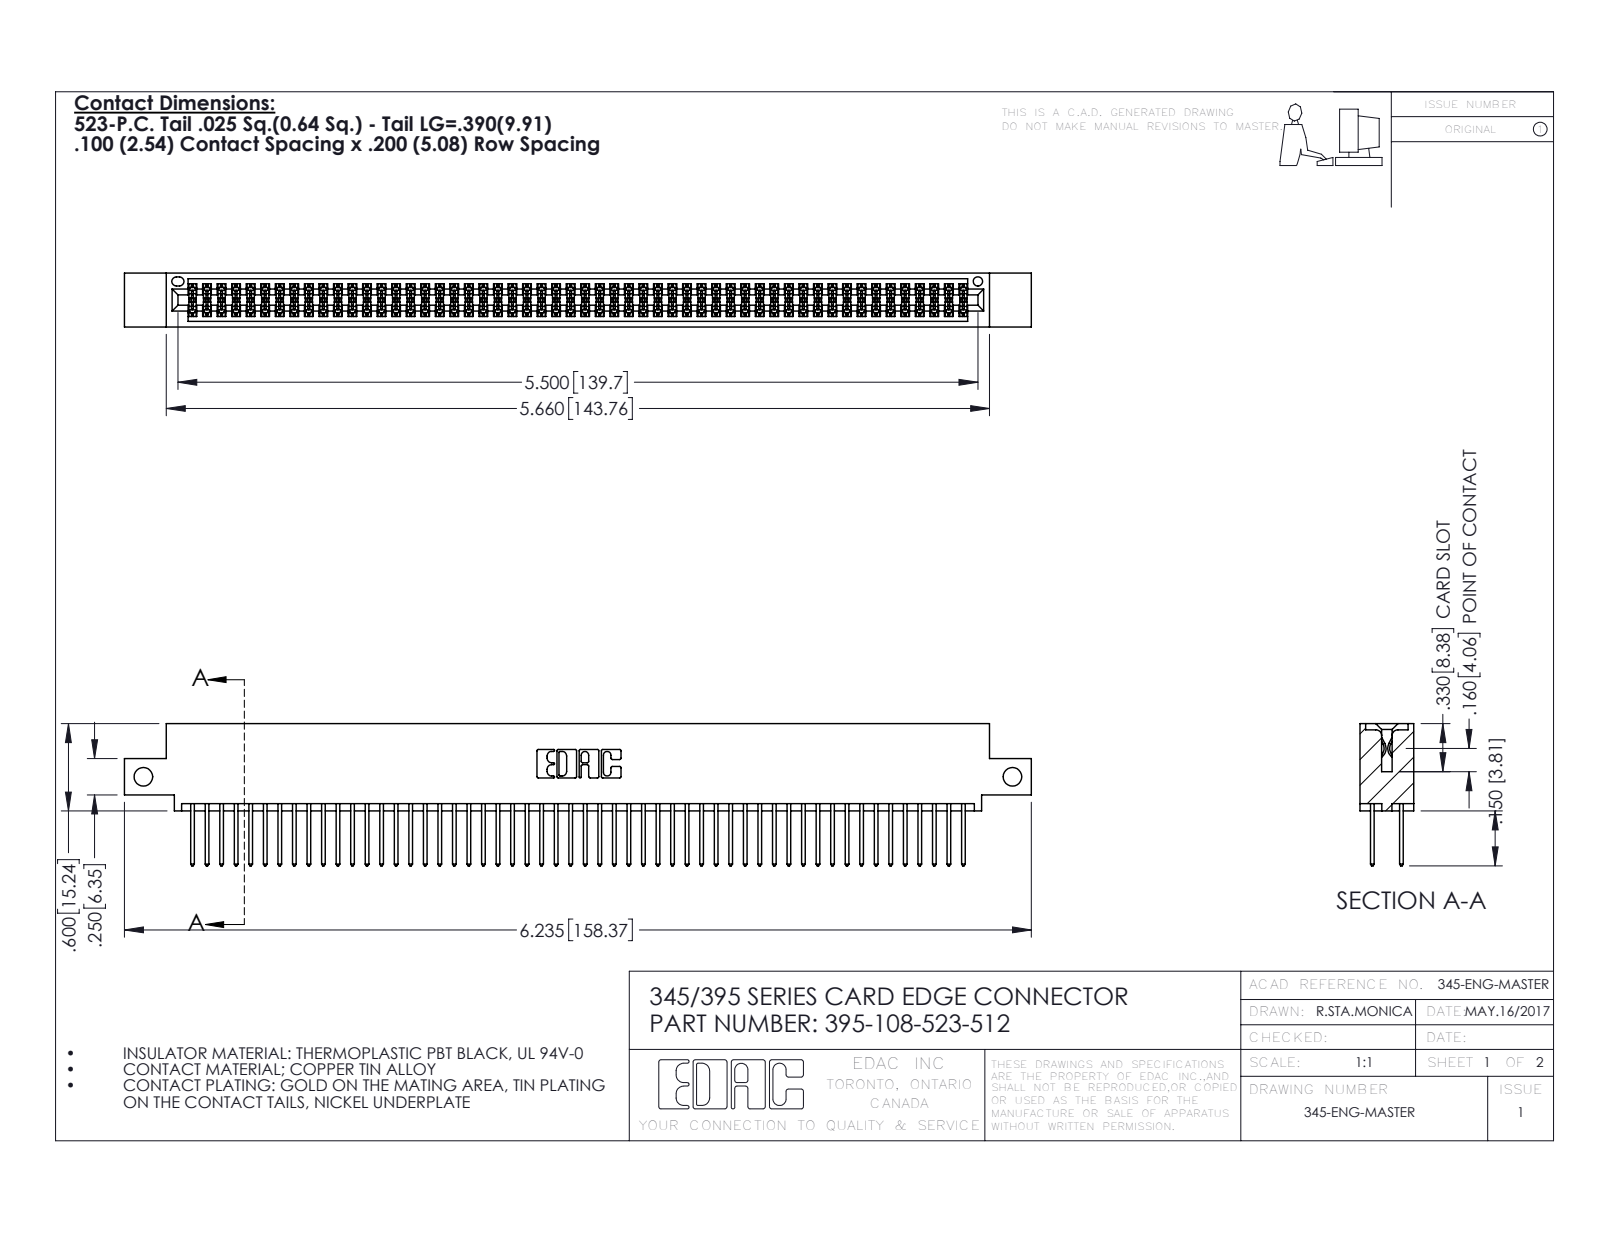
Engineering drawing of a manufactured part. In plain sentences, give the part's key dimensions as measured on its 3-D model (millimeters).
The part is named "395-108-523-512; 345-292-001_345-293-123; 345 Part_0.110 Offset - Side Mount". Its 3-D file was written by "SolidWorks 2016 (CONFIG_CONTROL_DESIGN)". It is 109 solids with 5530 faces: 3648 planar, 1882 cylindrical and 0 other. Overall it measures 158.4 by 24.8 by 9.4 millimeters. Its volume is 15 600 cubic millimeters and its surface area 24 170 square millimeters. Round holes: 2 of diameter 3.3, 1 of diameter 1.6. Partial cylindrical surfaces (rounded edges, fillets, slot ends): 162 of radius 0.2, 108 of radius 0.3, 22 of radius 0.3, 6 of radius 0.2, 6 of radius 0.8, 3 of radius 0.7, 2 of radius 0.4, 2 of radius 0.5. The main face-to-face distances are 7.6, 1.8, 5.1, 2.5, 6.9, 0.6, 9.4, 5.7, 4.4, 3.8. The hole center spacings are 151.8.
